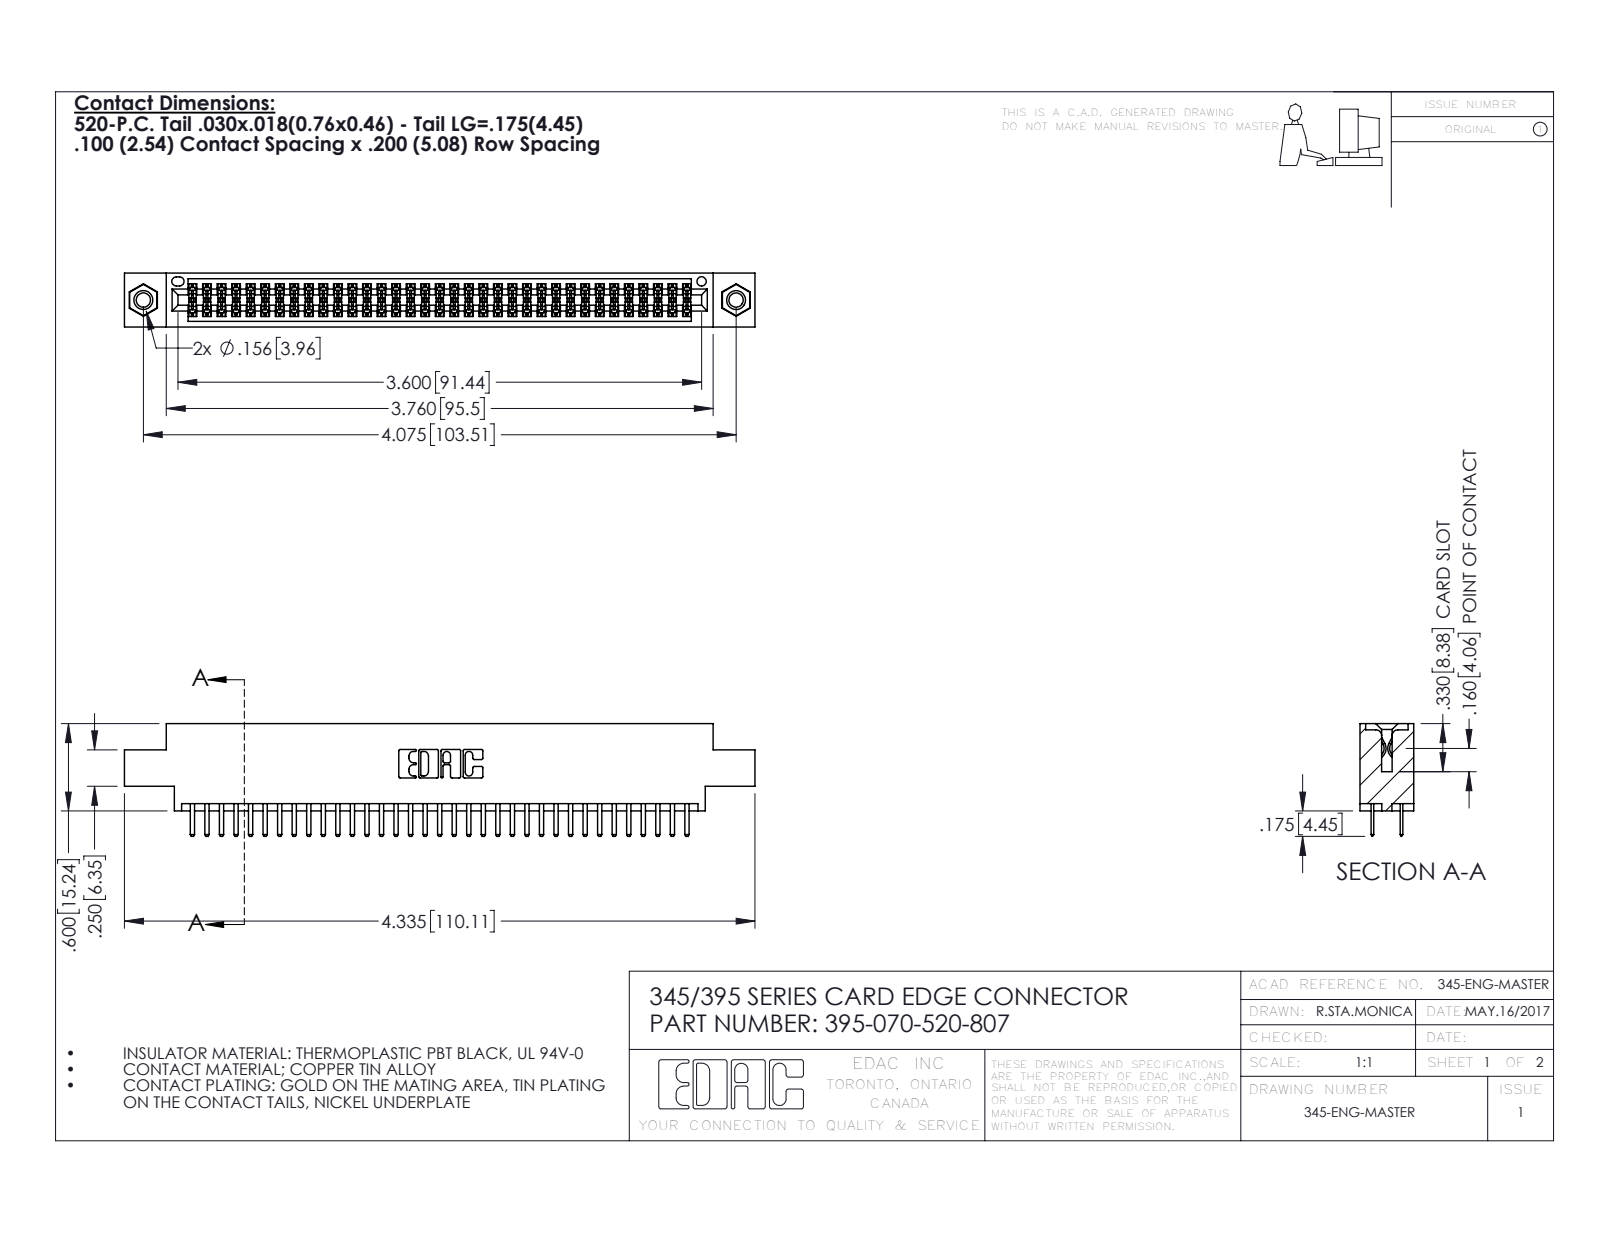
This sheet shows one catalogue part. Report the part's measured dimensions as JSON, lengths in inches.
{"part_name": "345-292-001_345-293-120; 345-250-001_345-250-005-103; 345 Part_0.170 Offset - 0.156 Dia-TI; 395-070-520-807", "step_written_by": "SolidWorks 2016 (CONFIG_CONTROL_DESIGN)", "units": "inches", "bodies": {"solids": 73, "faces": 3970, "planar": 2566, "cylindrical": 1388, "other": 16}, "overall_size": [4.335, 0.775, 0.37], "volume_in3": 0.639, "surface_area_in2": 23.95, "round_holes": [[0.098, 2], [0.125, 2], [0.156, 2], [0.064, 1]], "round_bosses_or_shafts": [[0.155, 2]], "partial_cylinders_radius": [[0.006, 105], [0.01, 74], [0.01, 22], [0.007, 6], [0.031, 6], [0.026, 3], [0.014, 2], [0.019, 2]], "face_to_face_distances": [0.072, 0.298, 0.2, 0.37, 0.098, 0.272, 0.025, 0.225, 0.022, 0.175], "hole_center_spacings": [0.27, 3.839, 4.075]}
